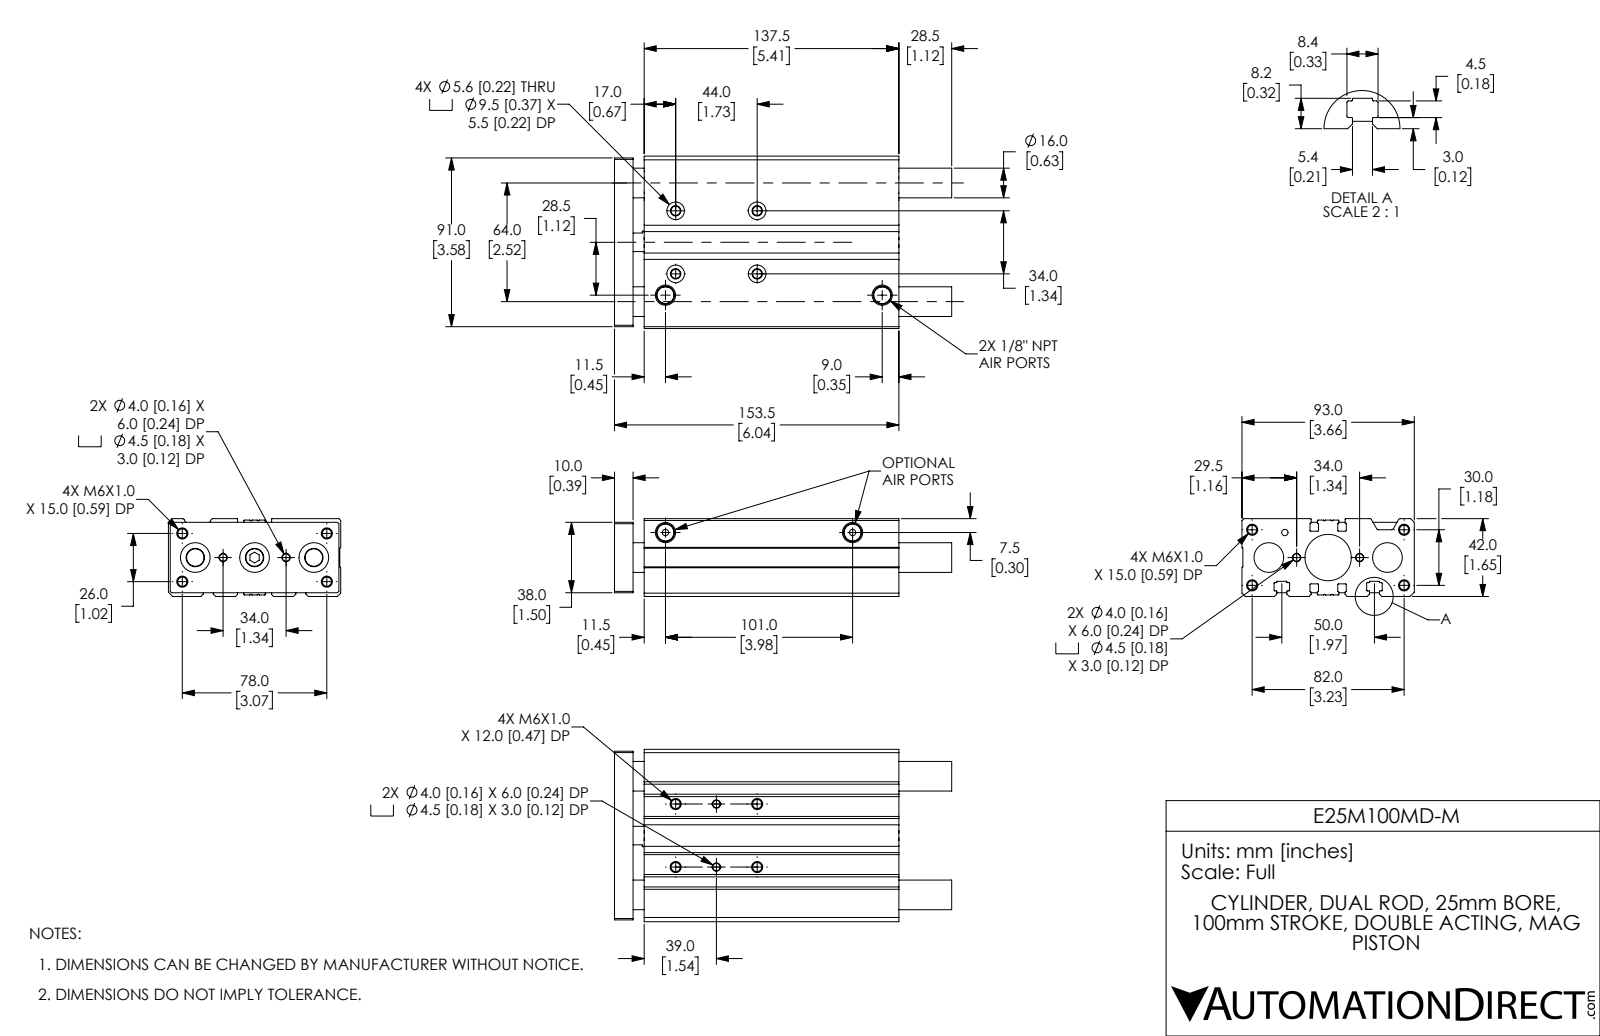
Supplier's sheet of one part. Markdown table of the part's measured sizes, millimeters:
| quantity | value |
| --- | --- |
| part name | E25M100MD-M; E25M100MD-M_BODY; E25M100MD-M_ENDPLATE |
| STEP written by | SolidWorks 2019 (CONFIG_CONTROL_DESIGN) |
| units | millimeters |
| bodies | 5 solids, 423 faces (139 planar, 190 cylindrical, 94 other) |
| overall size | 182 × 93 × 42 |
| volume | 489 507 mm³ |
| surface area | 124 962 mm² |
| round holes (diameter × count) | 4.92 × 8, 4 × 4, 4.5 × 4, 4.92 × 4, 5.6 × 4, 9.5 × 4, 8 × 3, 16 × 3, 3.43 × 2, 9.91 × 2, 3.43 × 1, 16 × 1 |
| round bosses / shafts (diameter × count) | 12 × 1, 9.91 × 1 |
| partial cylindrical surfaces (radius × count) | 0.2 × 32, 0.4 × 28, 1 × 4, 0.3 × 2 |
| main face-to-face distances | 42, 6, 93, 0.8, 34.4, 15, 35.2, 16, 10, 2 |
| hole center spacings | 2.83, 14.76, 17.49, 22, 25.55, 28.07, 28.3, 34 |
